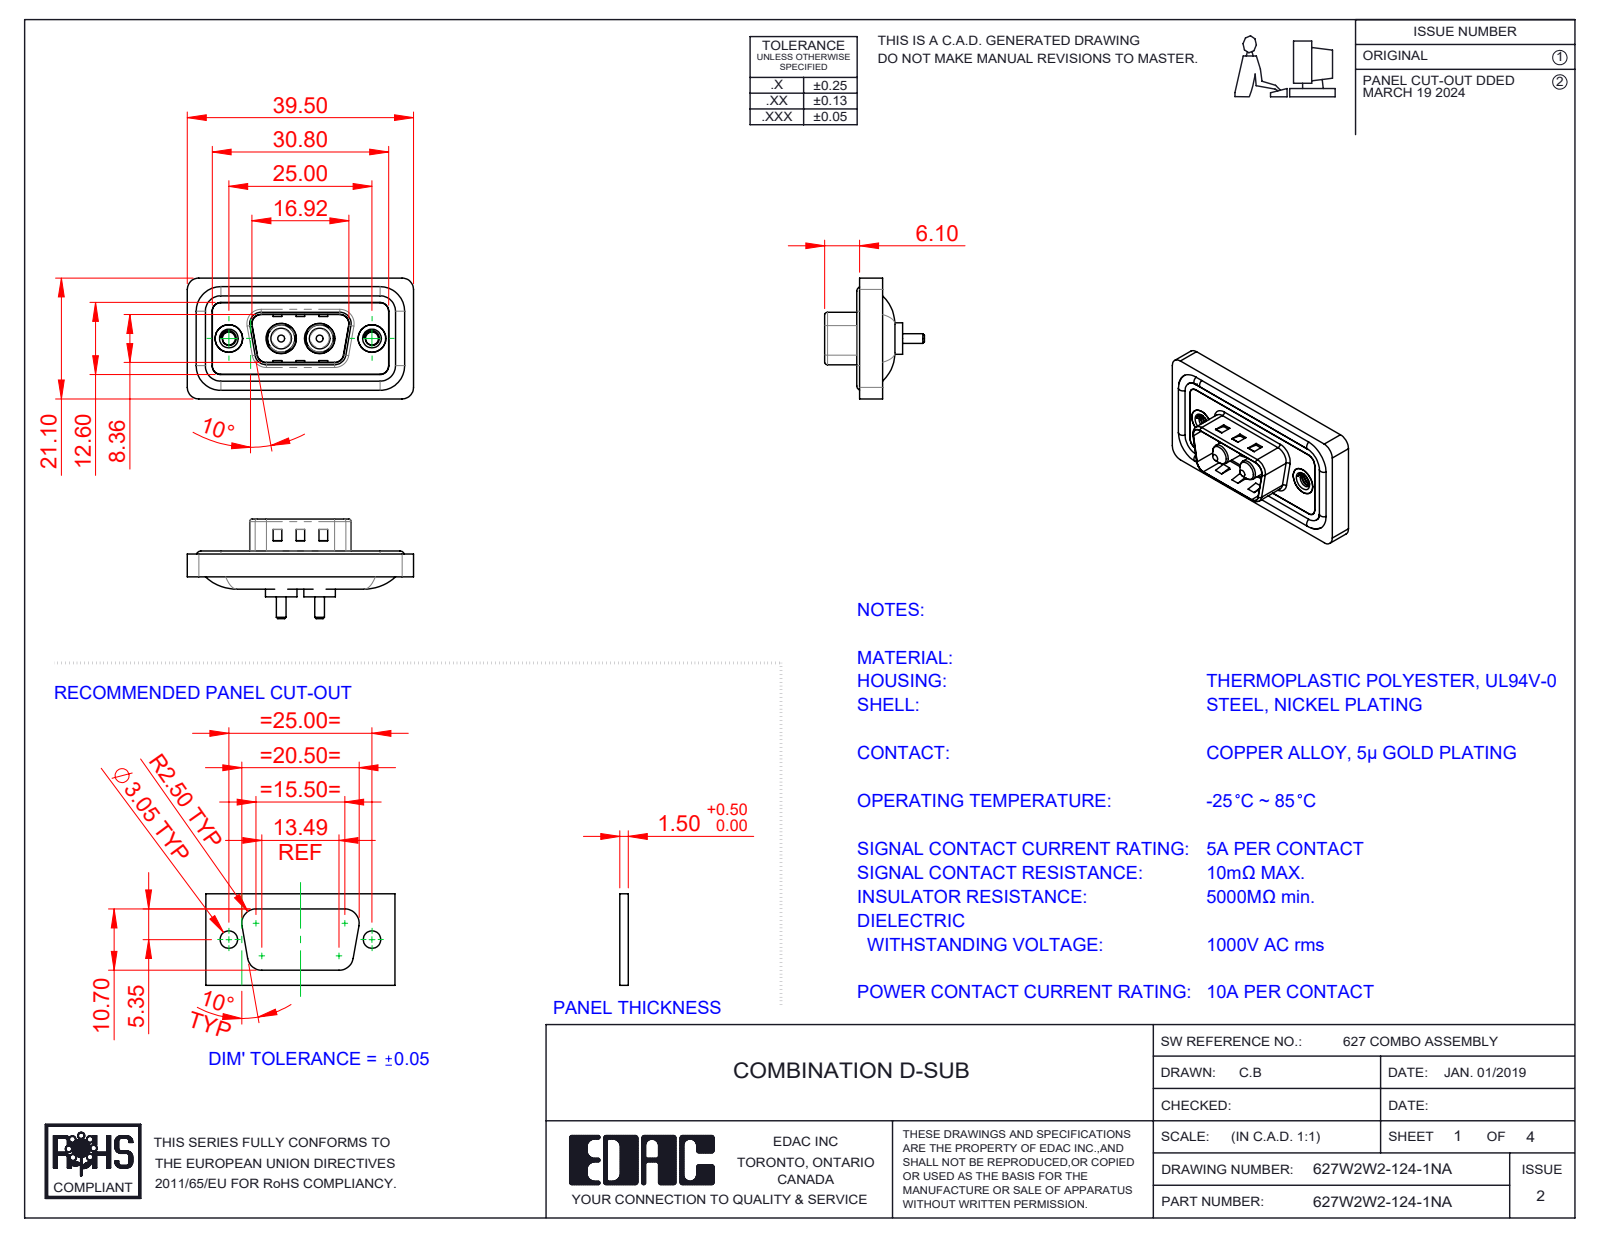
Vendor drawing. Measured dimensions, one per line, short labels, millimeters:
name: 627Combo Shell Front_09 Contacts; 627Combo Housing_2W2; 627Combo Shell Rear_09 Contacts; 627W2W2-124-1NA (+3 more)
written by: SolidWorks 2023 (CONFIG_CONTROL_DESIGN)
unit: mm
bodies: 11 solids, 487 faces (165 planar, 220 cylindrical, 102 other)
size: 39.5 × 21.1 × 17.4
volume: 4 433 mm³; area: 6 956 mm²
holes: 2× ⌀2.26, 2× ⌀4, 2× ⌀4.8, 2× ⌀4.85, 2× ⌀5, 2× ⌀5.3
bosses: 4× ⌀1.6, 2× ⌀5.5, 2× ⌀5.2, 2× ⌀4.9, 2× ⌀4.75, 2× ⌀3.75, 2× ⌀3.6, 2× ⌀1.7
rounds: 22× R1.5, 18× R2, 8× R0.5, 8× R1.6, 4× R0.25, 4× R0.6, 4× R0.65, 4× R0.9
face distances: 0.4, 1.1, 2.9, 3.1, 0.5, 1.5, 1.6, 4, 2.5, 0.7
hole spacings: 9.14, 15.86, 6.72, 25
